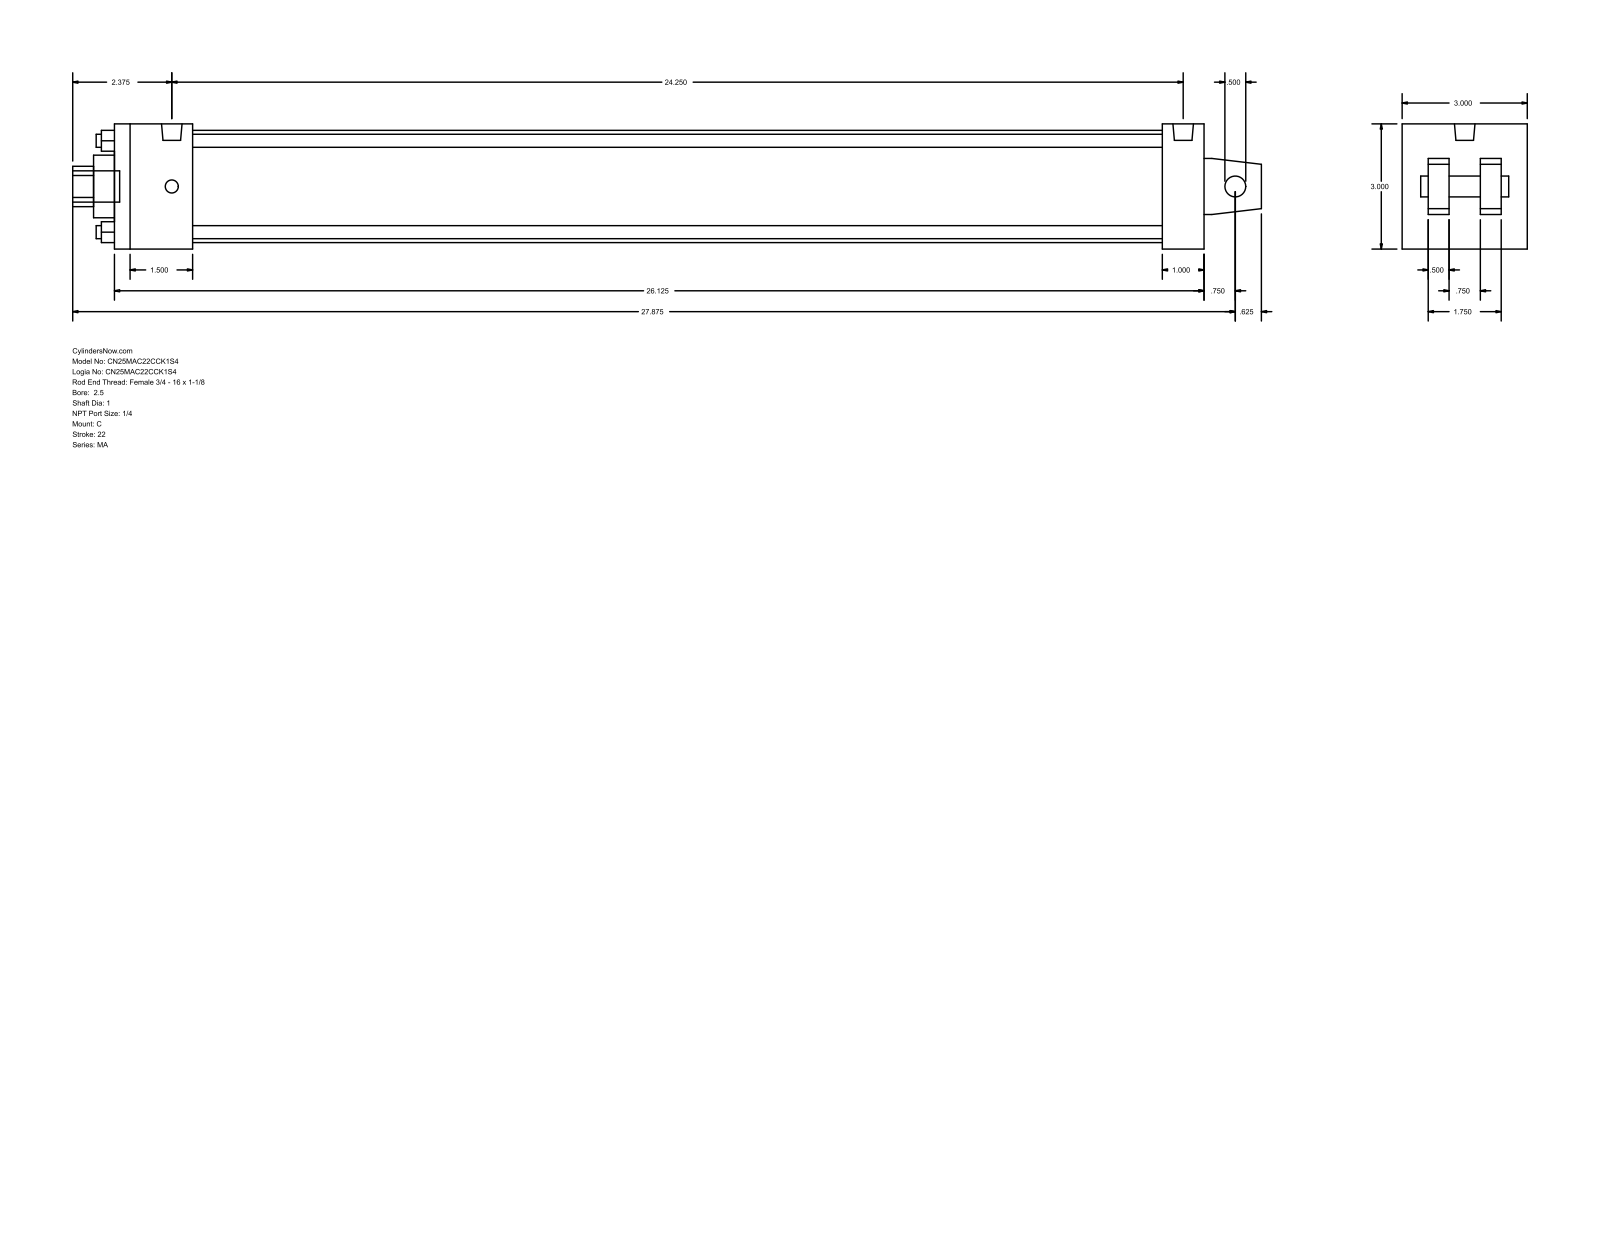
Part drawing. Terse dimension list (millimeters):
name: MA_C__0250_1
written by: GSSL Pune (CONFIG_CONTROL_DESIGN)
unit: mm
bodies: 0 solids, 103 faces (76 planar, 27 cylindrical, 0 other)
size: 723.9 × 76.2 × 76.2
holes: 4× ⌀7.94, 1× ⌀12.7, 1× ⌀25.4, 1× ⌀38.1, 1× ⌀68.33
bosses: 4× ⌀7.94, 2× ⌀12.49, 1× ⌀19.05
rounds: 1× R12.29
face distances: 76.2, 663.58, 47.63, 12.7, 15.87, 60.33, 25.4, 28.57, 638.18, 590.55
hole spacings: 39.33, 55.62, 78.66
